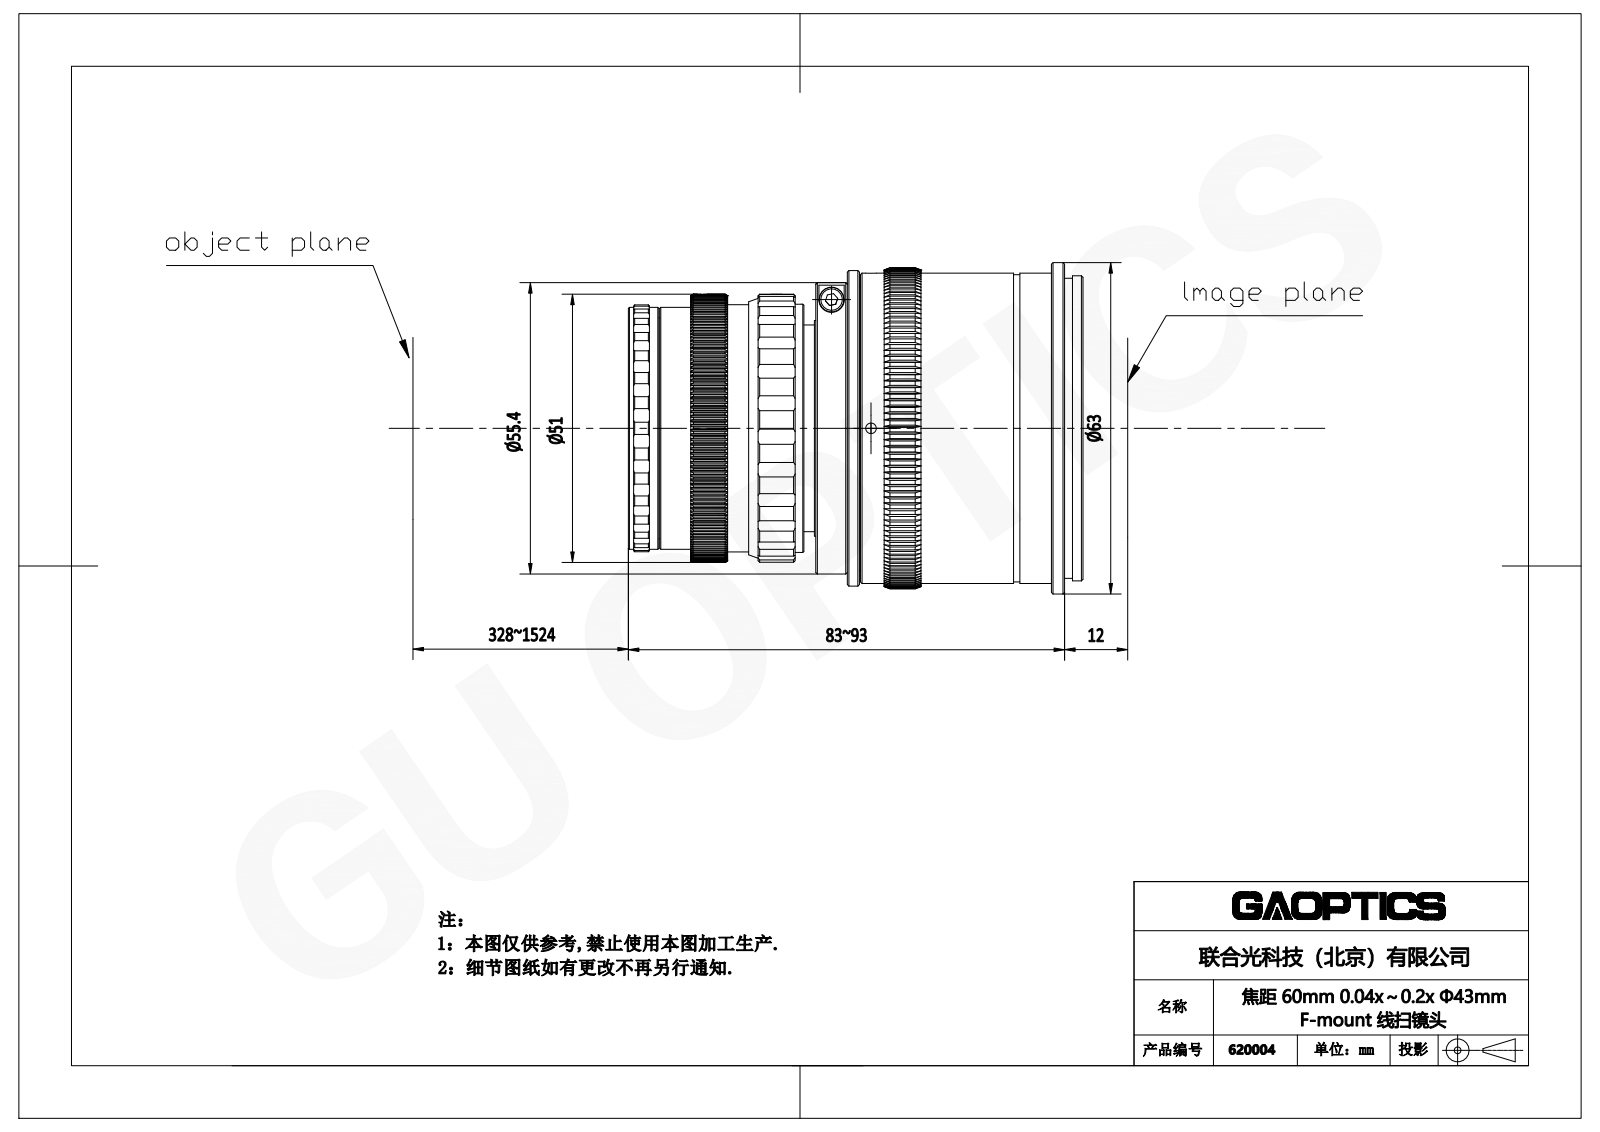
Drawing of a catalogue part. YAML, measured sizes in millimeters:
part_name: "前镜筒; 光阑限位压圈; M2.5x5 平头顶丝; M2x2.5 平头顶丝 (+3 more)"
step_written_by: "SolidWorks 2016 (AUTOMOTIVE_DESIGN)"
units: millimeters
bodies: {solids: 21, faces: 2924, planar: 941, cylindrical: 1003, other: 980}
overall_size: [86.43, 63, 63]
volume: 98690
surface_area: 77114
round_holes:
  - {diameter: 2, count: 5}
  - {diameter: 1.3, count: 2}
  - {diameter: 1.4, count: 1}
  - {diameter: 2.6, count: 1}
  - {diameter: 11, count: 1}
  - {diameter: 12.8, count: 1}
  - {diameter: 16.17, count: 1}
  - {diameter: 18, count: 1}
  - {diameter: 21, count: 1}
  - {diameter: 21.2, count: 1}
  - {diameter: 24, count: 1}
  - {diameter: 25.4, count: 1}
round_bosses_or_shafts:
  - {diameter: 2.5, count: 2}
  - {diameter: 2, count: 2}
  - {diameter: 63, count: 1}
  - {diameter: 60, count: 1}
  - {diameter: 59, count: 1}
  - {diameter: 58.4, count: 1}
  - {diameter: 58, count: 1}
  - {diameter: 57.05, count: 1}
partial_cylinders:
  - {radius: 0.15, count: 180}
  - {radius: 2.5, count: 55}
  - {radius: 1, count: 7}
  - {radius: 5, count: 4}
  - {radius: 1.25, count: 2}
  - {radius: 0.75, count: 1}
  - {radius: 1.75, count: 1}
  - {radius: 2.4, count: 1}
face_to_face_distances: [6, 12.8, 2.5, 6.8, 17.56, 10.76, 4.5, 49.56, 21.23, 27.23]
hole_center_spacings: [16.5, 4, 14.01, 14.05, 18.01, 18.05, 32.06, 33]
